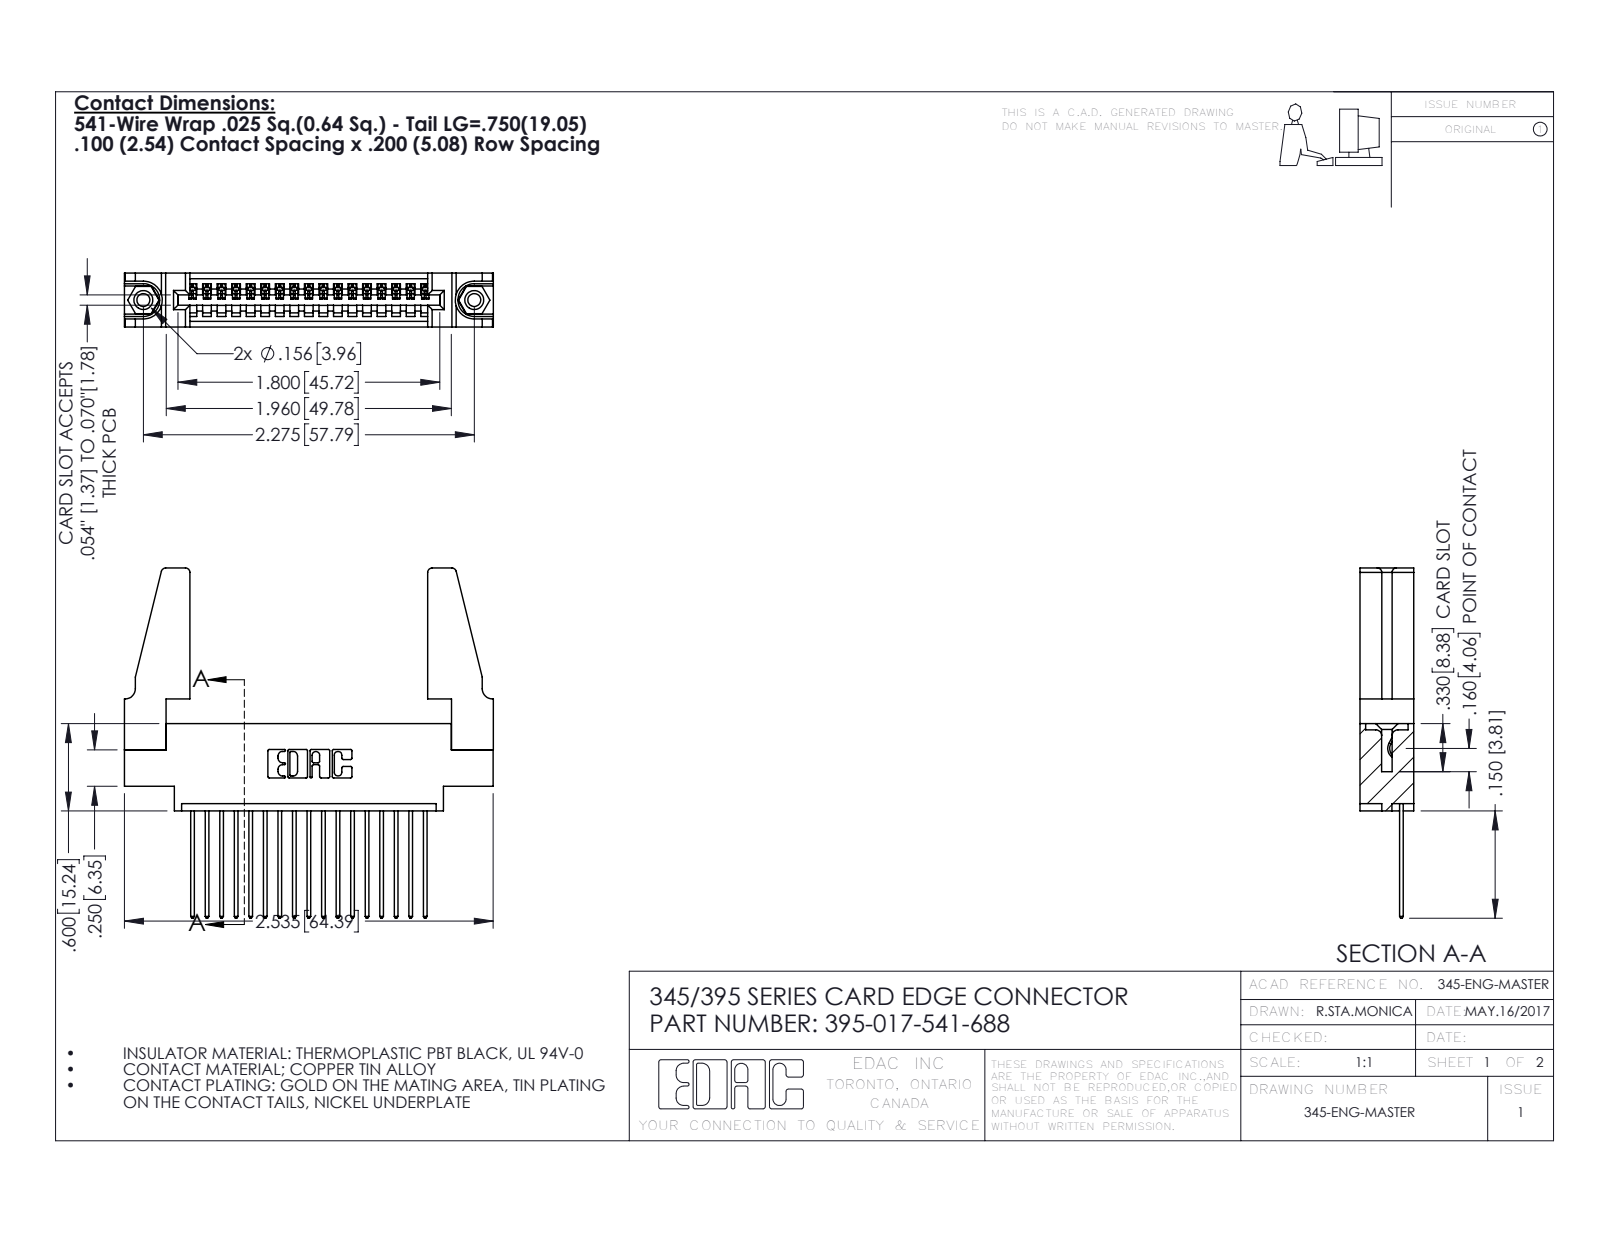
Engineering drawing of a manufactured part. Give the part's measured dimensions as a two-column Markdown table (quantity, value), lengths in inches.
| quantity | value |
| --- | --- |
| part name | 395-017-541-688; 345-220-078_345-220-088; 345 Part_0.170 Offset - 0.156 Dia-TH; 345-250-001_345-250-001-102 (+1 more) |
| STEP written by | SolidWorks 2016 (CONFIG_CONTROL_DESIGN) |
| units | inches |
| bodies | 22 solids, 1240 faces (836 planar, 388 cylindrical, 16 other) |
| overall size | 2.536 × 2.407 × 0.37 |
| volume | 0.556 in³ |
| surface area | 17.09 in² |
| round holes (diameter × count) | 0.089 × 2, 0.125 × 2, 0.156 × 2, 0.064 × 1 |
| round bosses / shafts (diameter × count) | 0.155 × 2 |
| partial cylindrical surfaces (radius × count) | 0.006 × 34, 0.01 × 34, 0.01 × 22, 0.03 × 8, 0.007 × 6, 0.031 × 6, 0.026 × 3, 0.031 × 2 |
| main face-to-face distances | 0.37, 0.072, 0.298, 0.098, 0.272, 0.025, 0.2, 0.225, 0.15, 0.148 |
| hole center spacings | 0.27, 2.041, 2.275 |
